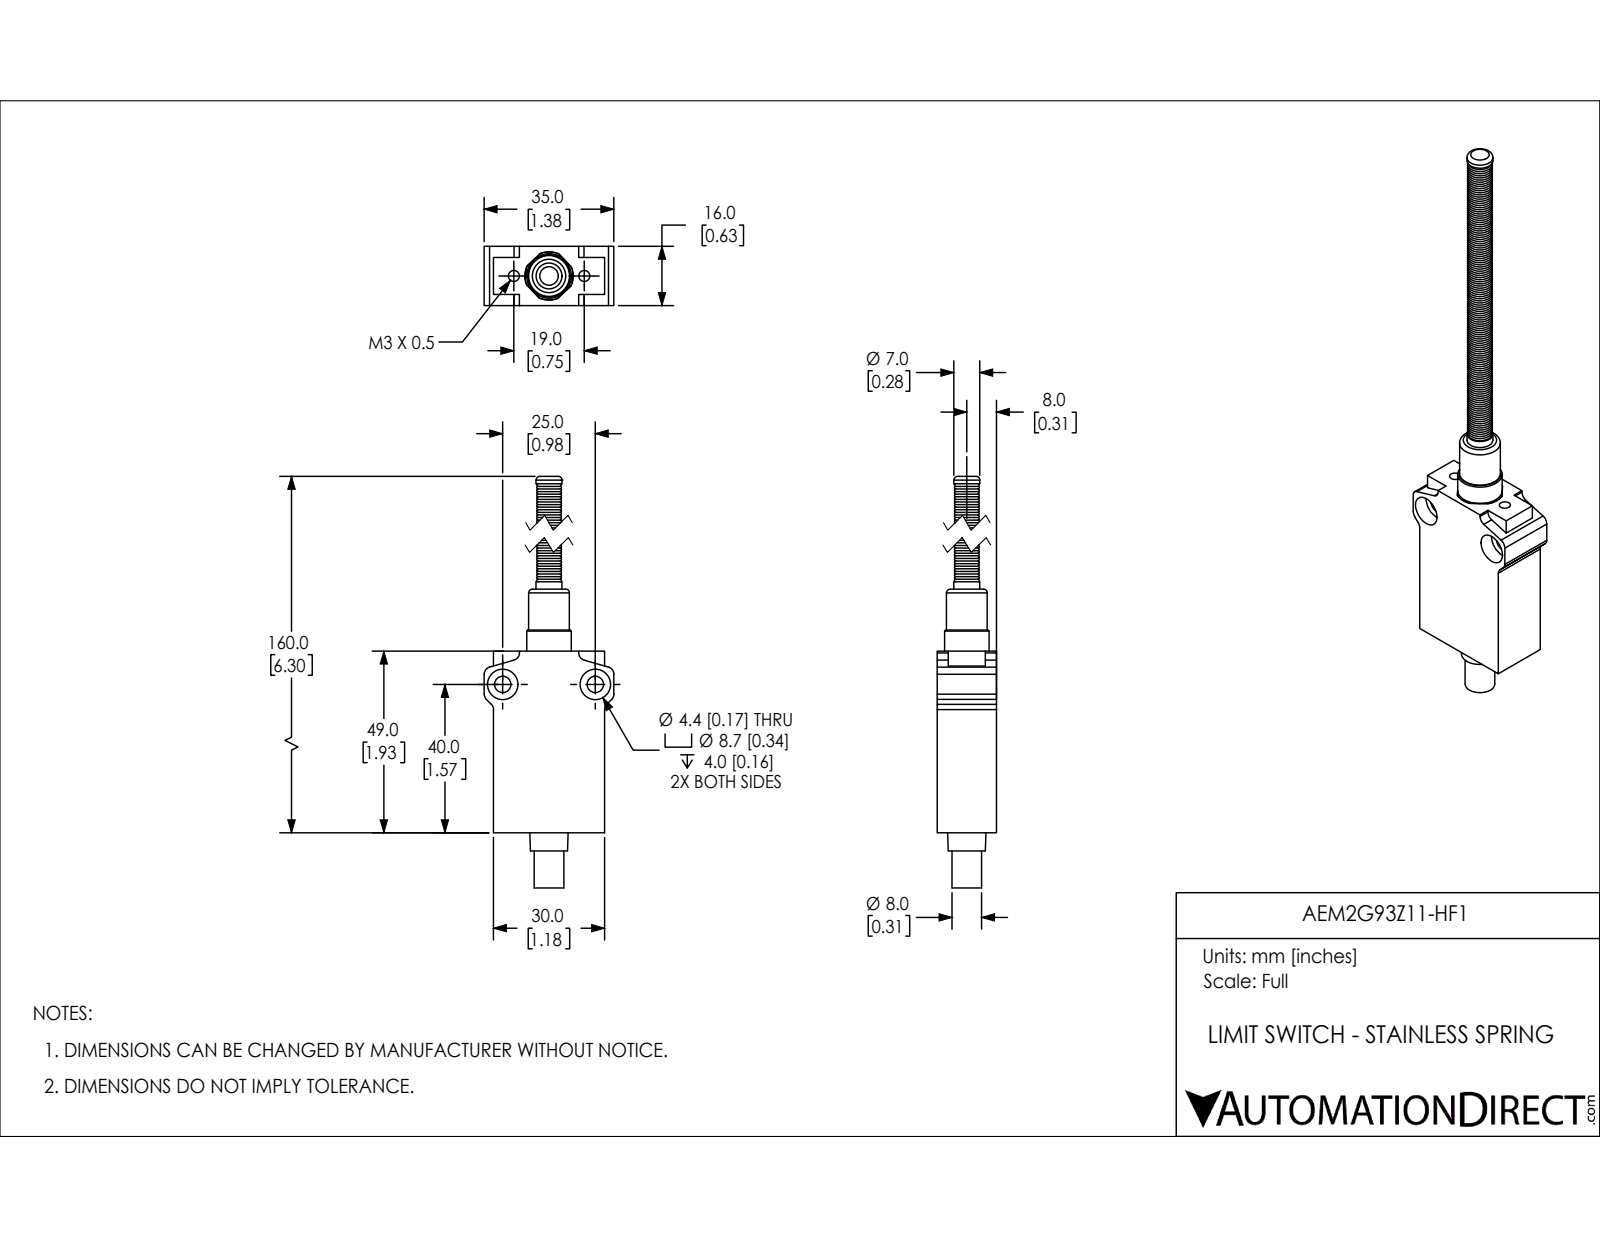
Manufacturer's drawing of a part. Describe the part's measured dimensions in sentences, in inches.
The part is named "AEM2G93Z11-HF1". Its 3-D file was written by "SolidWorks 2018 (AUTOMOTIVE_DESIGN)". It is 4 solids with 388 faces: 54 planar, 61 cylindrical and 273 other. Overall it measures 6.886 by 1.378 by 0.63 inches. Its volume is 1.752 cubic inches and its surface area 17.08 square inches. Round holes: 2 of diameter 0.118, 2 of diameter 0.173, 2 of diameter 0.323. Round bosses or shafts: 1 of diameter 0.472, 1 of diameter 0.433, 1 of diameter 0.315, 1 of diameter 0.276, 1 of diameter 0.197. Partial cylindrical surfaces (rounded edges, fillets, slot ends): 8 of radius 0.079, 1 of radius 0.256. The main face-to-face distances are 0.63, 1.181, 1.929, 1.74, 0.189, 0.472, 0.098, 1.28, 0.157, 0.118. The hole center spacings are 0.748, 0.984.
